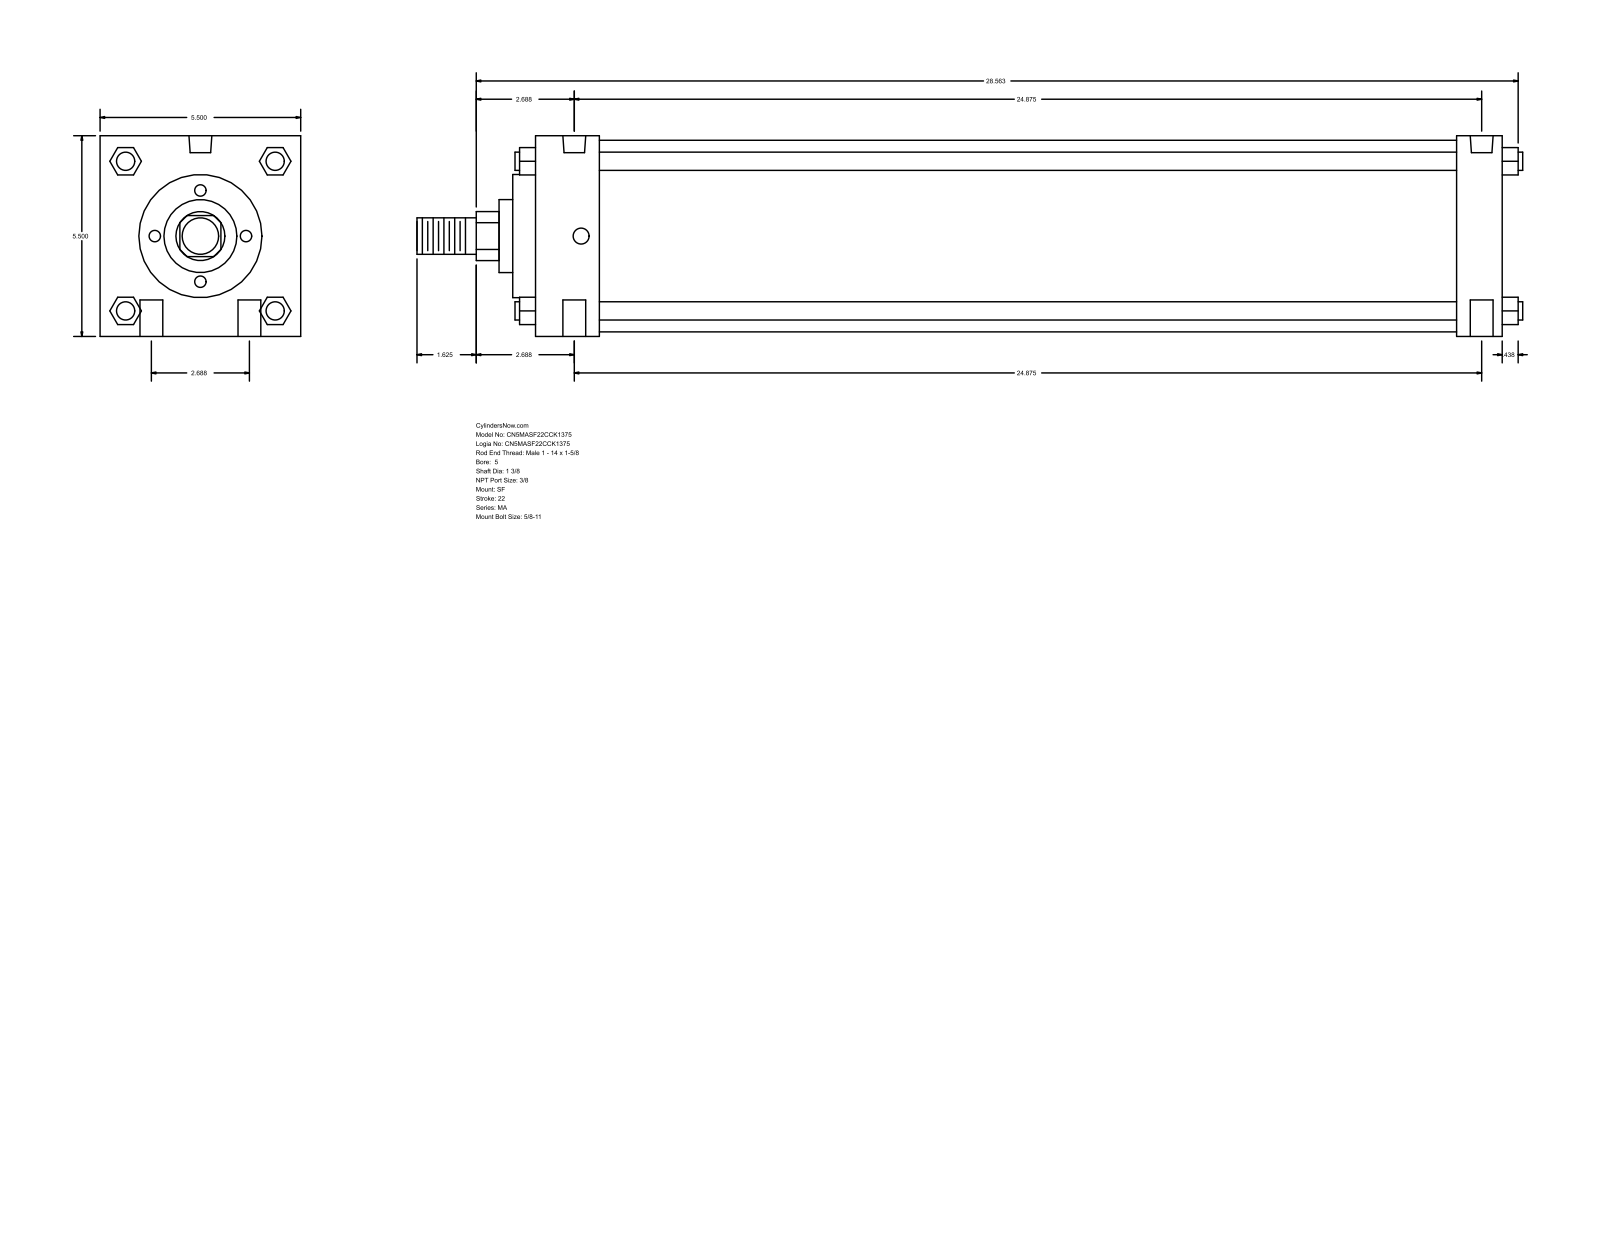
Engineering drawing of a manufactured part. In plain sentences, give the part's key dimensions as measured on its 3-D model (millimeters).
The part is named "MA_SF__0500_1.375". Its 3-D file was written by "GSSL Pune (CONFIG_CONTROL_DESIGN)". It is 0 solids with 126 faces: 95 planar, 31 cylindrical and 0 other. Overall it measures 769.94 by 139.7 by 139.7 millimeters. Round holes: 4 of diameter 15.88, 2 of diameter 11.11, 2 of diameter 15.93. Round bosses or shafts: 4 of diameter 12.7, 1 of diameter 133.35, 1 of diameter 85.72, 1 of diameter 50.8, 1 of diameter 34.92, 1 of diameter 25.4. Partial cylindrical surfaces (rounded edges, fillets, slot ends): 1 of radius 17.06. The main face-to-face distances are 139.7, 673.11, 44.45, 641.35, 596.9, 628.66, 31.76, 15.87, 60.32, 657.22. The hole center spacings are 34.13, 632.75, 631.83, 68.26, 635.51, 622.3.
